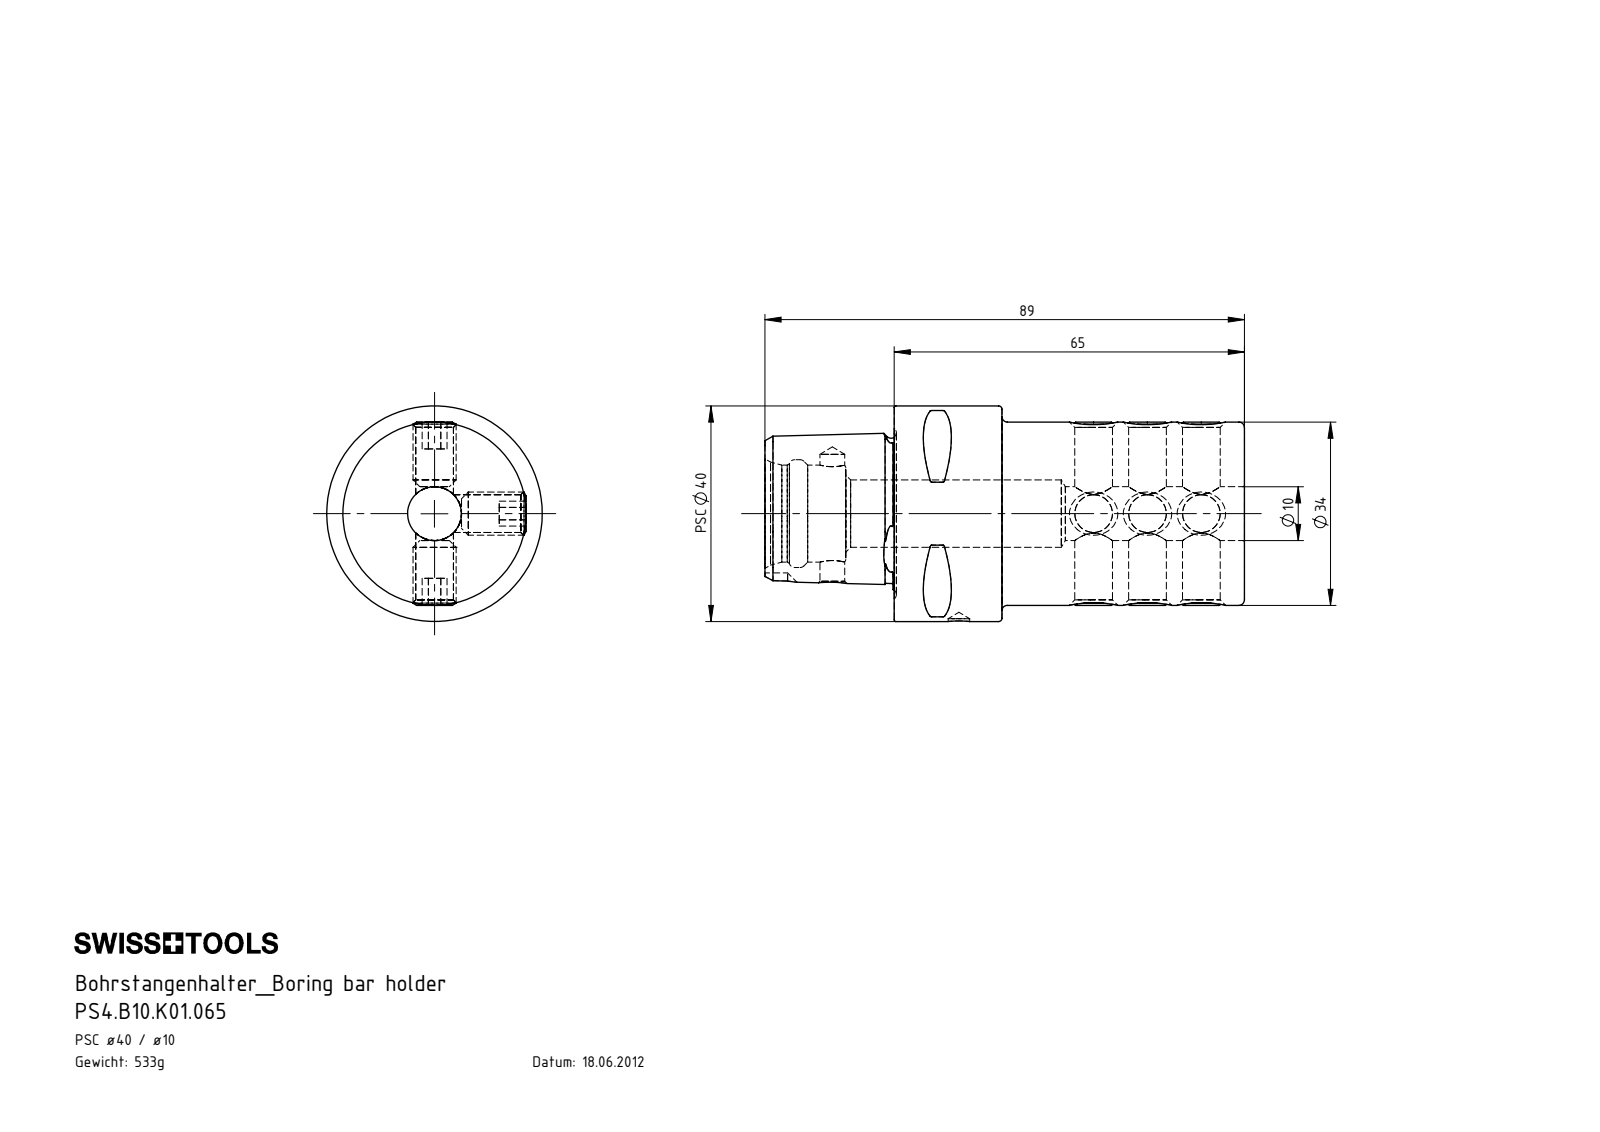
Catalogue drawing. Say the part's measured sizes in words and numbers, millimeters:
The part is named "PS4.B10.K01.065; ISO 4026 - M8 x 12_PreviewCfg; PS4-B10.K01.065_A". Its 3-D file was written by "SolidWorks 2017 (AUTOMOTIVE_DESIGN)". It is 10 solids with 308 faces: 101 planar, 65 cylindrical and 142 other. Overall it measures 89 by 40 by 40 millimeters. Its volume is 67 934 cubic millimeters and its surface area 20 850 square millimeters. Round holes: 6 of diameter 7, 1 of diameter 4, 1 of diameter 4.6, 1 of diameter 10, 1 of diameter 12.5, 1 of diameter 18, 1 of diameter 20. Round bosses or shafts: 6 of diameter 8, 1 of diameter 40, 1 of diameter 34. Partial cylindrical surfaces (rounded edges, fillets, slot ends): 8 of radius 0.3, 1 of radius 3. The main face-to-face distances are 65, 5, 10, 4, 20, 24, 9, 45, 44, 12. The hole center spacings are 10, 20, 23.5, 25, 35, 45, 48.5, 58.5.
